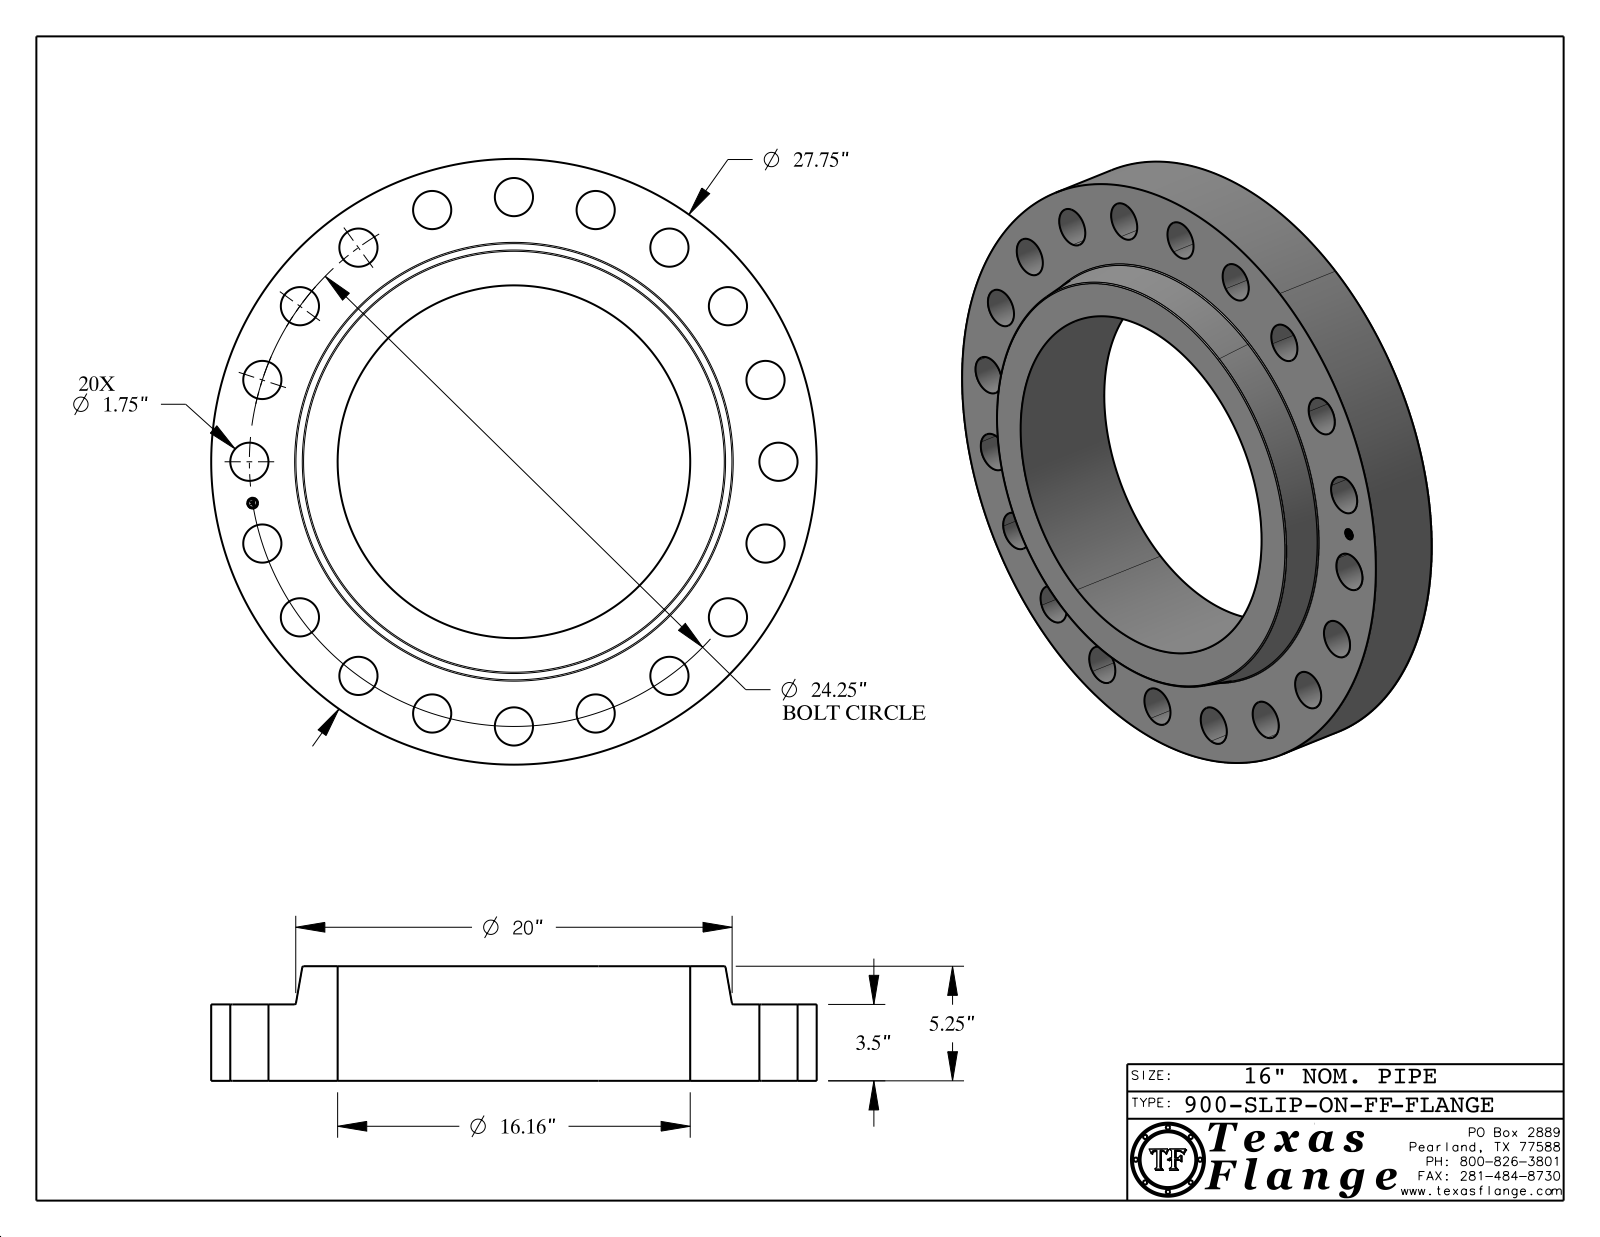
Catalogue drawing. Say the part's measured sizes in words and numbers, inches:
The part is named "900-SLIP-ON-FF". Its 3-D file was written by "CATIA V5 STEP AP214 (AUTOMOTIVE_DESIGN)". It is 1 solid with 438 faces: 368 planar, 64 cylindrical and 6 other. Overall it measures 27.75 by 27.75 by 5.25 inches. Its volume is 1 405 cubic inches and its surface area 1 749 square inches. Round holes: 20 of diameter 1.75, 1 of diameter 0.495, 1 of diameter 16.16. Round bosses or shafts: 8 of diameter 0.03, 1 of diameter 27.75, 1 of diameter 0.39. The main face-to-face distances are 3.5, 5.25, 1.75, 3.485, 0.015, 1.765, 0.148, 0.145, 0.027, 0.096. The hole center spacings are 17.147, 23.063, 19.619, 12.125, 3.794, 7.494, 11.009, 14.254.
